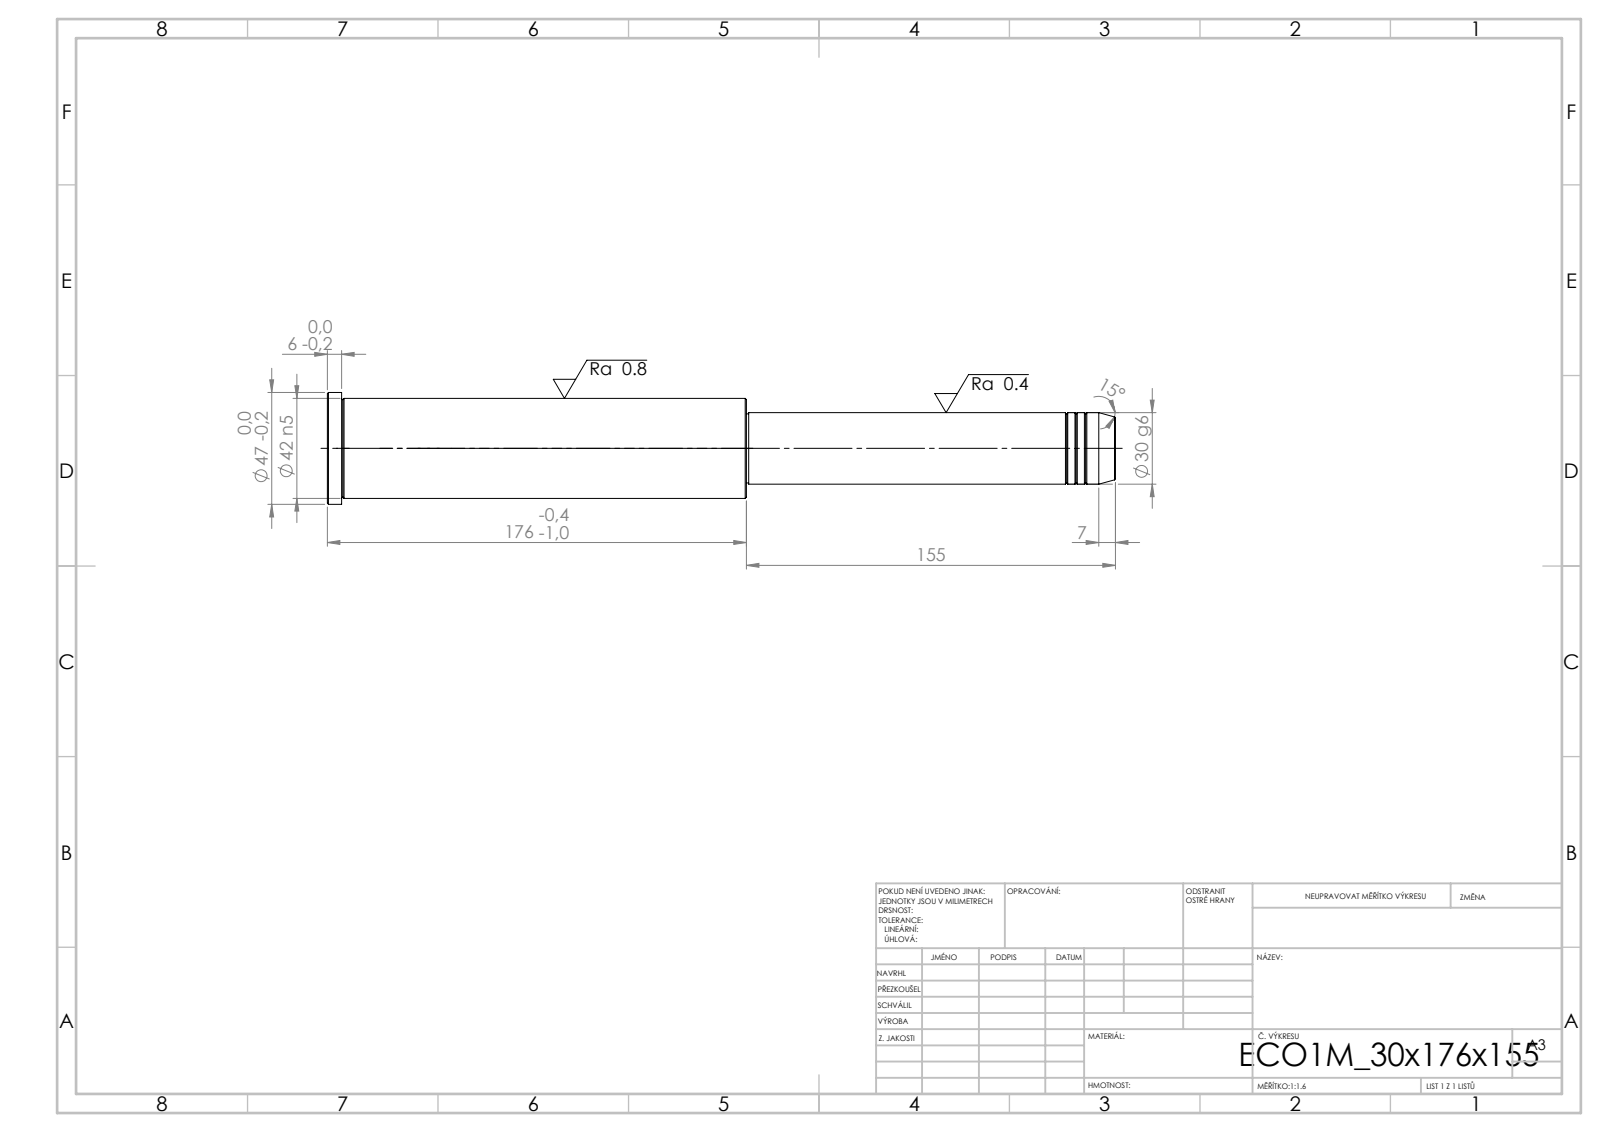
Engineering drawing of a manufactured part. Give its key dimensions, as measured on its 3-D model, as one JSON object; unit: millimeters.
{"step_written_by": "SolidWorks 2019 (CONFIG_CONTROL_DESIGN)", "units": "millimeters", "bodies": {"solids": 1, "faces": 43, "planar": 5, "cylindrical": 14, "other": 24}, "overall_size": [331, 47, 47], "volume_mm3": 354661, "surface_area_mm2": 41432, "round_bosses_or_shafts": [[47, 1], [42, 1], [30, 1], [29, 1]], "face_to_face_distances": [176, 155, 331, 325, 170, 6, 154, 1, 171, 177]}
